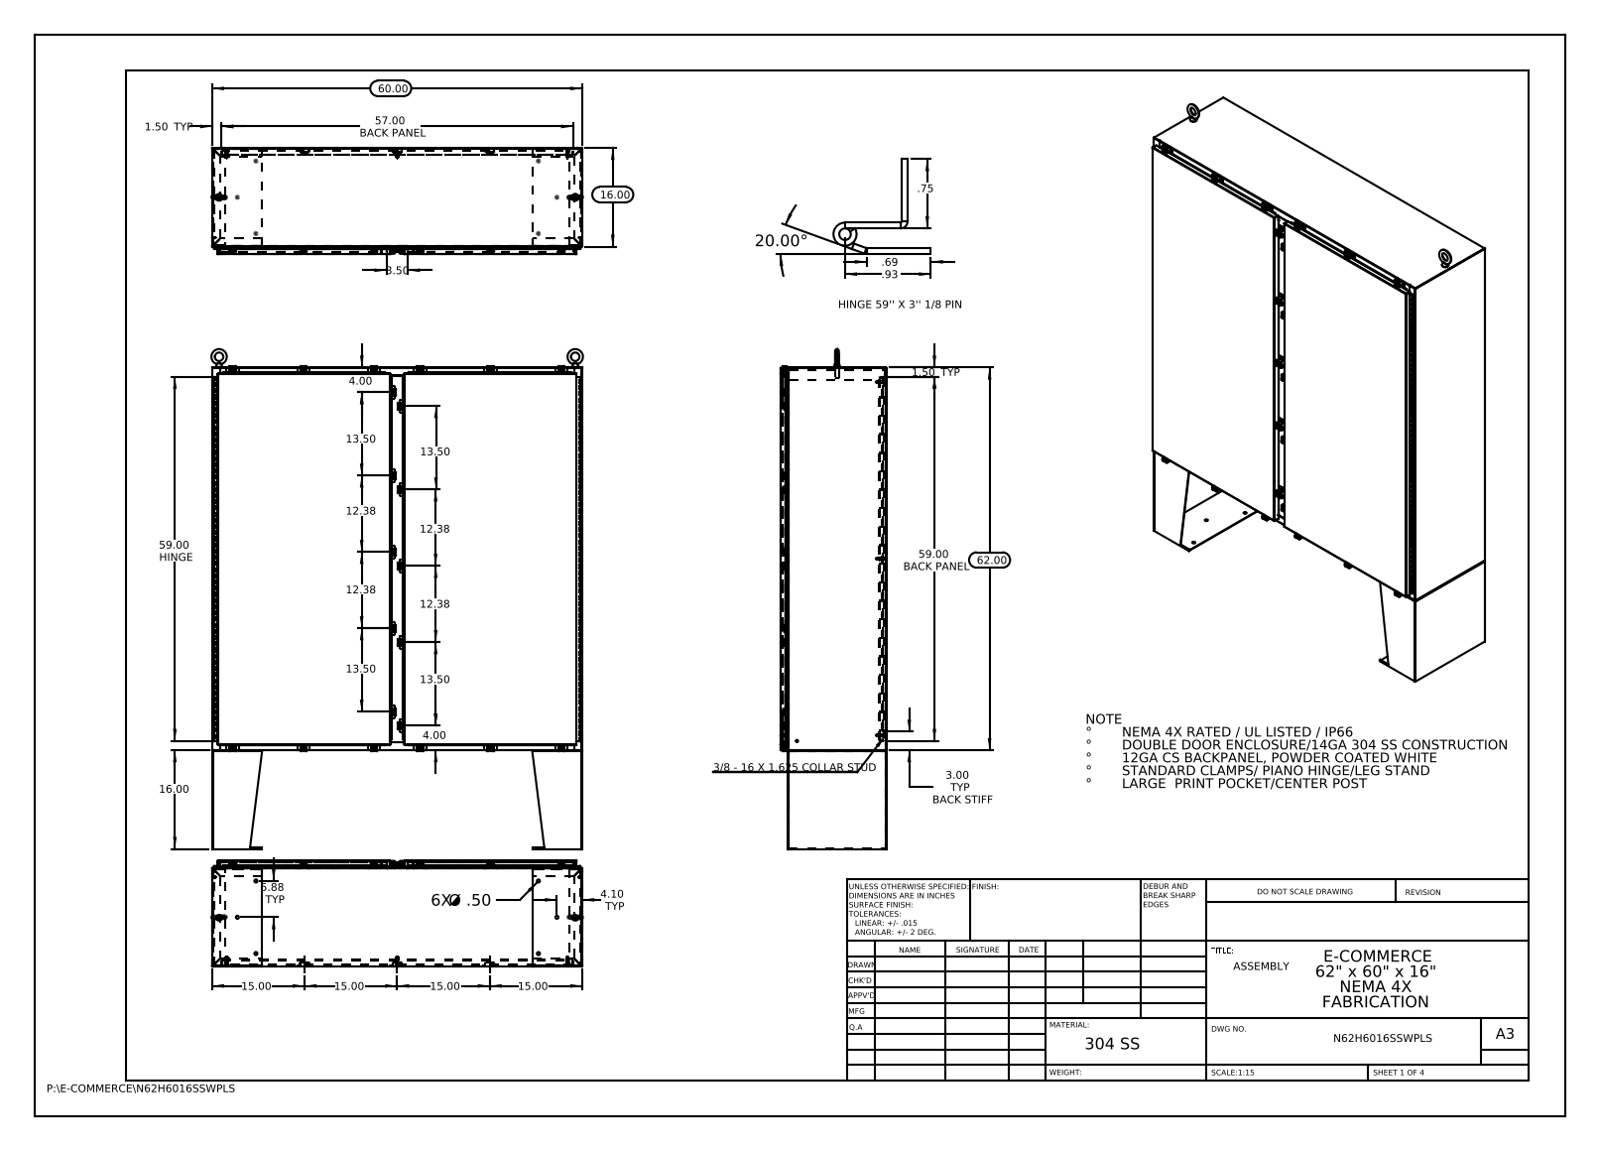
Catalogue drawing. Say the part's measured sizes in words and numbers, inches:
The part is named "N62H6016SSWPLS Enclosure Stiffener 14 GA; N62H6016SSWPLS Hinge_DoubleDoor; N62H6016SSWPLS Eye-Bolt_Stiffener; N62H6016SSWPLS Left Cover (+8 more)". Its 3-D file was written by "SolidWorks 2013 (CONFIG_CONTROL_DESIGN)". It is 144 solids with 6444 faces: 3354 planar, 2762 cylindrical and 328 other. Overall it measures 81 by 60.226 by 17.201 inches. Its volume is 1 502 cubic inches and its surface area 36 479 square inches. Round holes: 22 of diameter 0.213, 22 of diameter 0.26, 14 of diameter 0.5, 4 of diameter 0.75, 2 of diameter 0.125, 2 of diameter 0.125. Round bosses or shafts: 24 of diameter 0.25, 22 of diameter 0.5, 22 of diameter 0.399, 10 of diameter 0.625, 8 of diameter 0.375, 8 of diameter 0.33, 3 of diameter 0.315, 3 of diameter 0.236. Partial cylindrical surfaces (rounded edges, fillets, slot ends): 96 of radius 0.06, 48 of radius 0.013, 44 of radius 0.12, 44 of radius 0.141, 40 of radius 0.088, 32 of radius 0.05, 32 of radius 0.08, 32 of radius 0.09. The main face-to-face distances are 0.075, 17.126, 0.104, 1.075, 17.051, 1, 16.126, 17.201, 16.051, 1.179. The hole center spacings are 61.431, 68.531, 2.608, 4.293, 8.377, 11.437, 11.438, 12.612.
